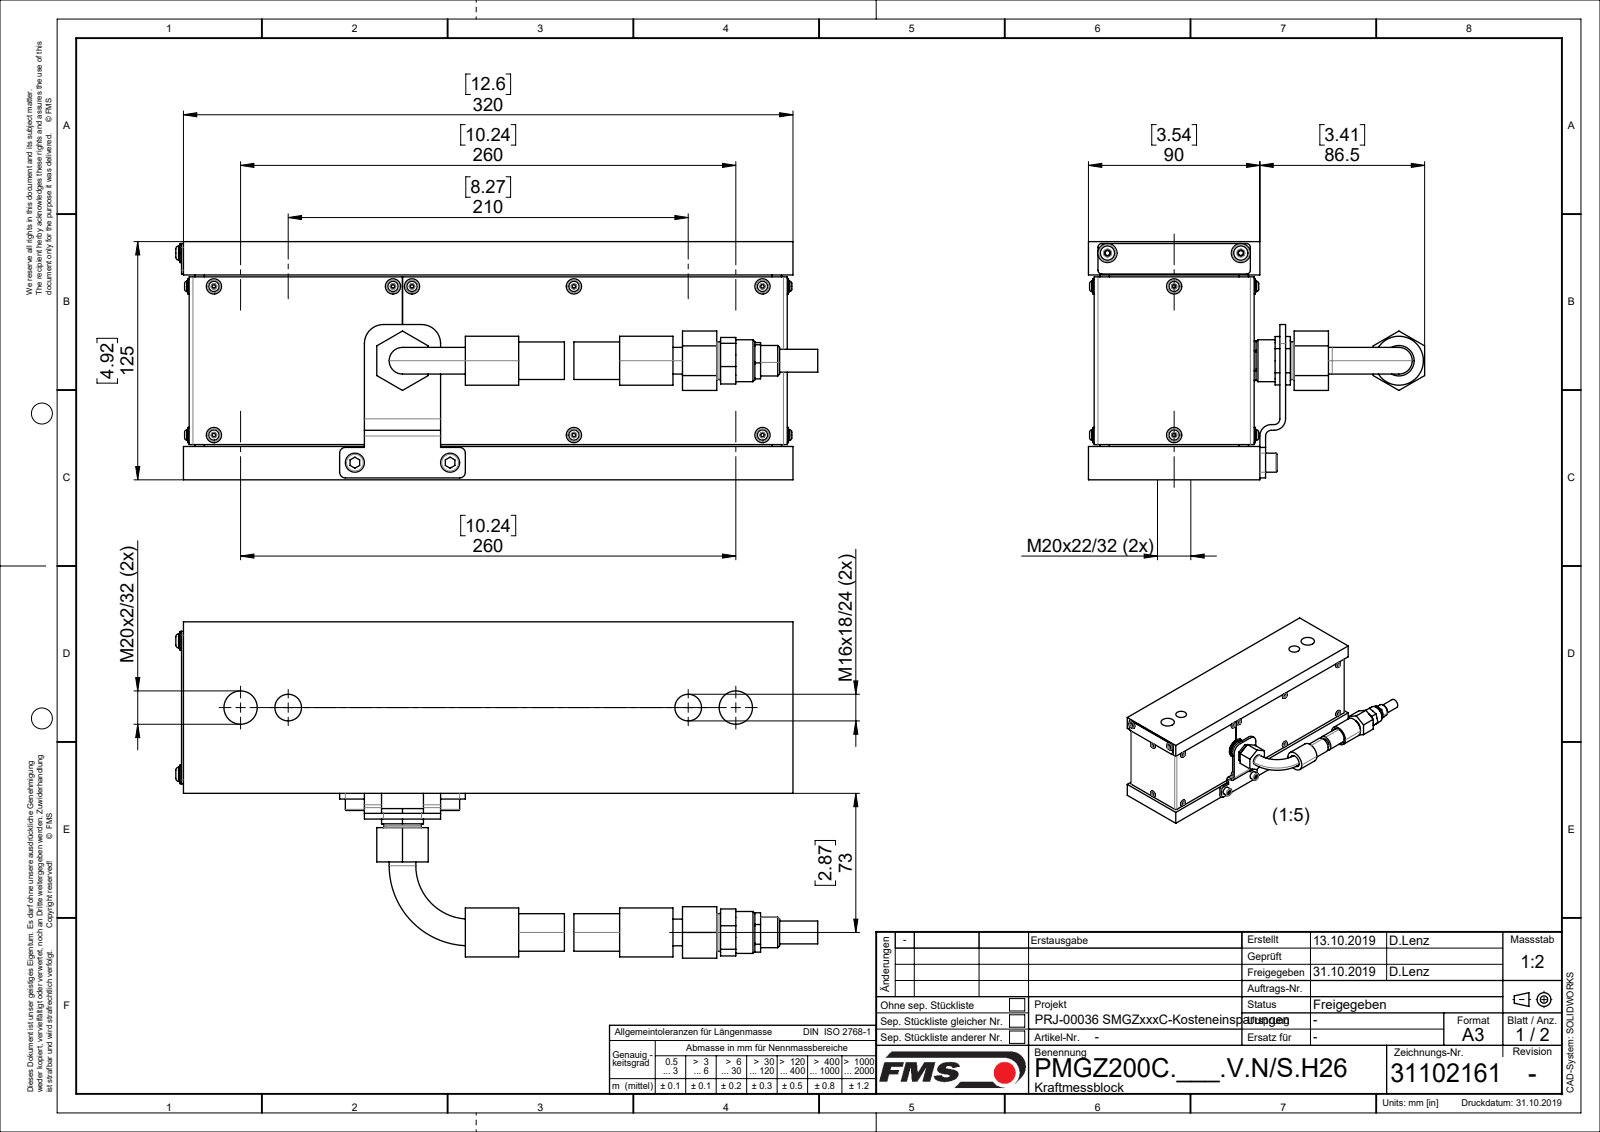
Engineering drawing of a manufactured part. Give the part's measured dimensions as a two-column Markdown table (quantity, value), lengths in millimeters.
| quantity | value |
| --- | --- |
| part name | 31101655_01; 31101507_stp_01; Ls-Schr eco-fix BN10649_M4x8; 31101654_01 (+8 more) |
| STEP written by | SolidWorks 2018 (CONFIG_CONTROL_DESIGN) |
| units | millimeters |
| bodies | 53 solids, 1677 faces (390 planar, 1035 cylindrical, 252 other) |
| overall size | 337 × 176.5 × 125 |
| volume | 3 343 000 mm³ |
| surface area | 544 490 mm² |
| round holes (diameter × count) | 4 × 21, 2.5 × 18, 5.4 × 18, 14 × 4, 10 × 3, 3.3 × 2, 4.2 × 2, 5 × 2, 6.5 × 2, 7.5 × 2, 9 × 2, 12 × 2 |
| round bosses / shafts (diameter × count) | 8 × 18, 3 × 18, 10 × 4, 22 × 2, 19.7 × 2, 17 × 2, 15.5 × 2, 6 × 2 |
| partial cylindrical surfaces (radius × count) | 0.29 × 264, 0.4 × 24, 1 × 20, 2 × 16, 3 × 6, 6 × 2, 10 × 2 |
| main face-to-face distances | 1, 2, 81, 3, 80, 82, 79, 83, 78, 84 |
| hole center spacings | 5, 78.16, 78, 90, 119.1, 10, 59.55, 39.32 |
